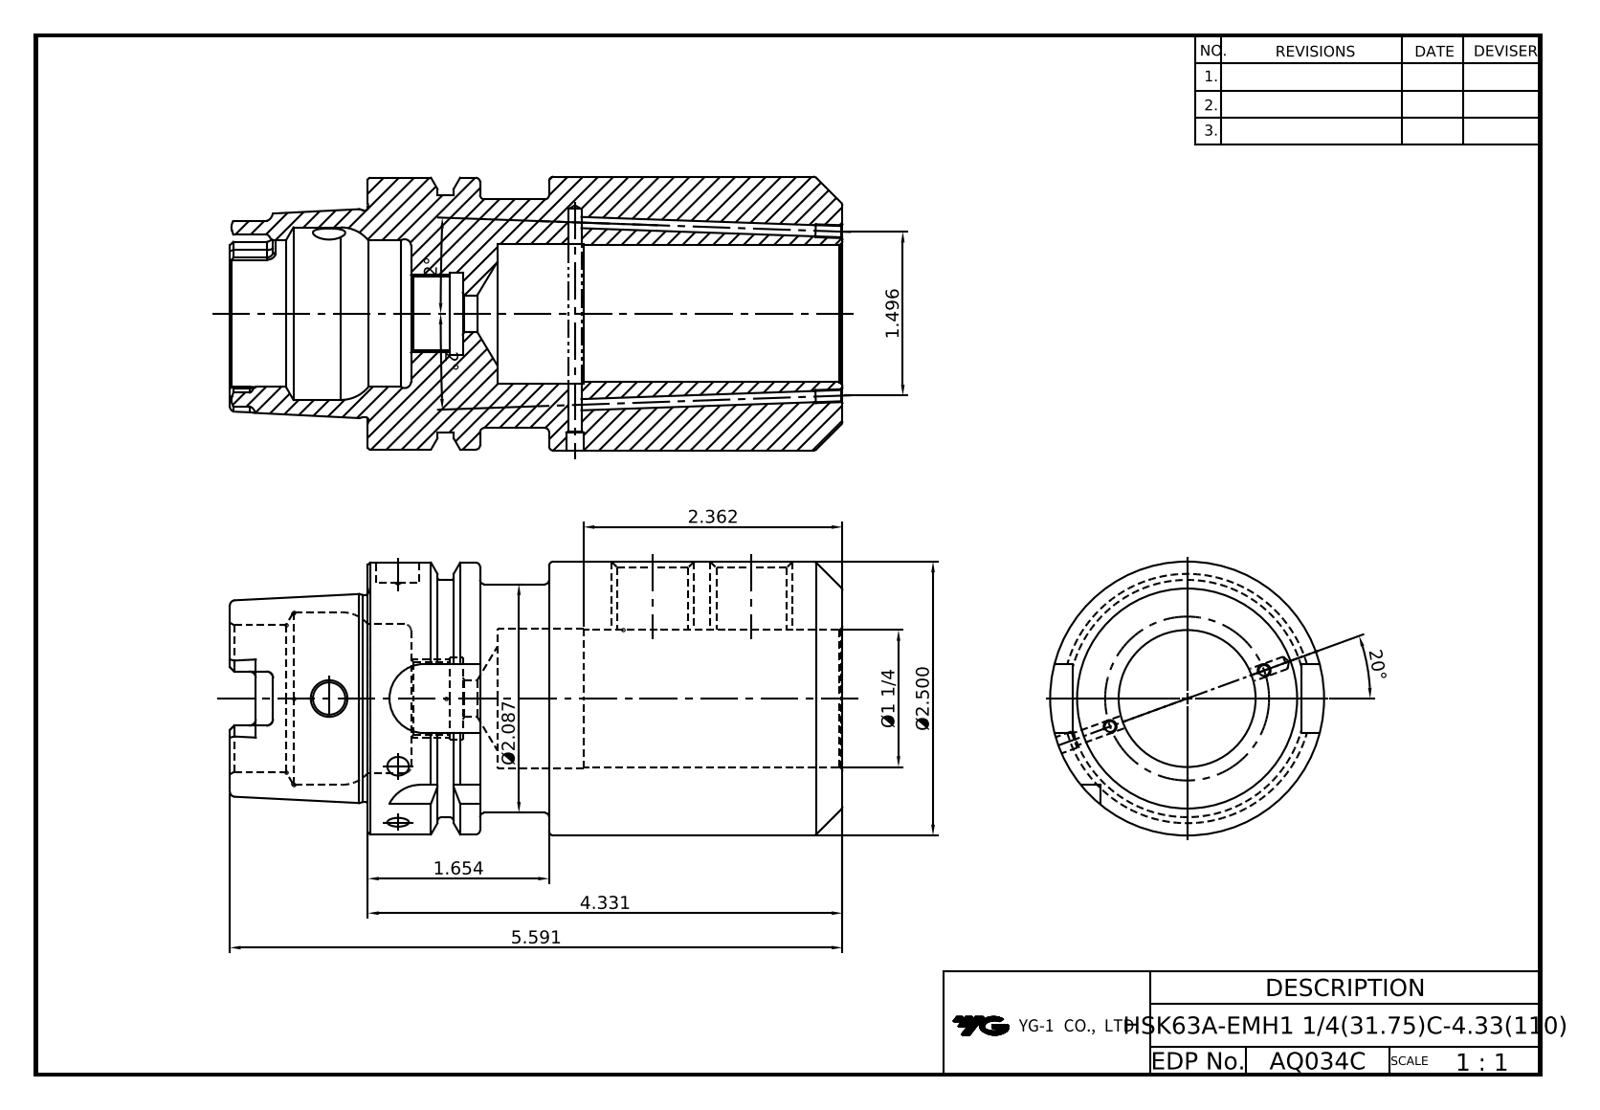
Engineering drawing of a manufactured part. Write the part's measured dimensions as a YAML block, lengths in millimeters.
part_name: "LO-HSK63A-EMH31.75C-110"
step_written_by: "Autodesk Inventor 2022 (AUTOMOTIVE_DESIGN)"
units: millimeters
bodies: {solids: 1, faces: 127, planar: 44, cylindrical: 38, other: 45}
overall_size: [142, 63.5, 63.5]
volume: 255401
surface_area: 49545
round_holes:
  - {diameter: 2.46, count: 2}
  - {diameter: 17.32, count: 2}
  - {diameter: 7.5, count: 1}
  - {diameter: 8.4, count: 1}
  - {diameter: 10, count: 1}
  - {diameter: 16.92, count: 1}
  - {diameter: 19, count: 1}
  - {diameter: 31.75, count: 1}
  - {diameter: 32.95, count: 1}
  - {diameter: 34, count: 1}
  - {diameter: 40, count: 1}
round_bosses_or_shafts:
  - {diameter: 63.5, count: 1}
  - {diameter: 63, count: 1}
  - {diameter: 55, count: 1}
  - {diameter: 53, count: 1}
  - {diameter: 48.04, count: 1}
partial_cylinders:
  - {radius: 1.5, count: 6}
  - {radius: 2.88, count: 4}
  - {radius: 8, count: 4}
face_to_face_distances: [16, 42, 12, 32, 110, 4, 20, 68, 30, 80]
hole_center_spacings: [22.86, 59.04, 81.9]
